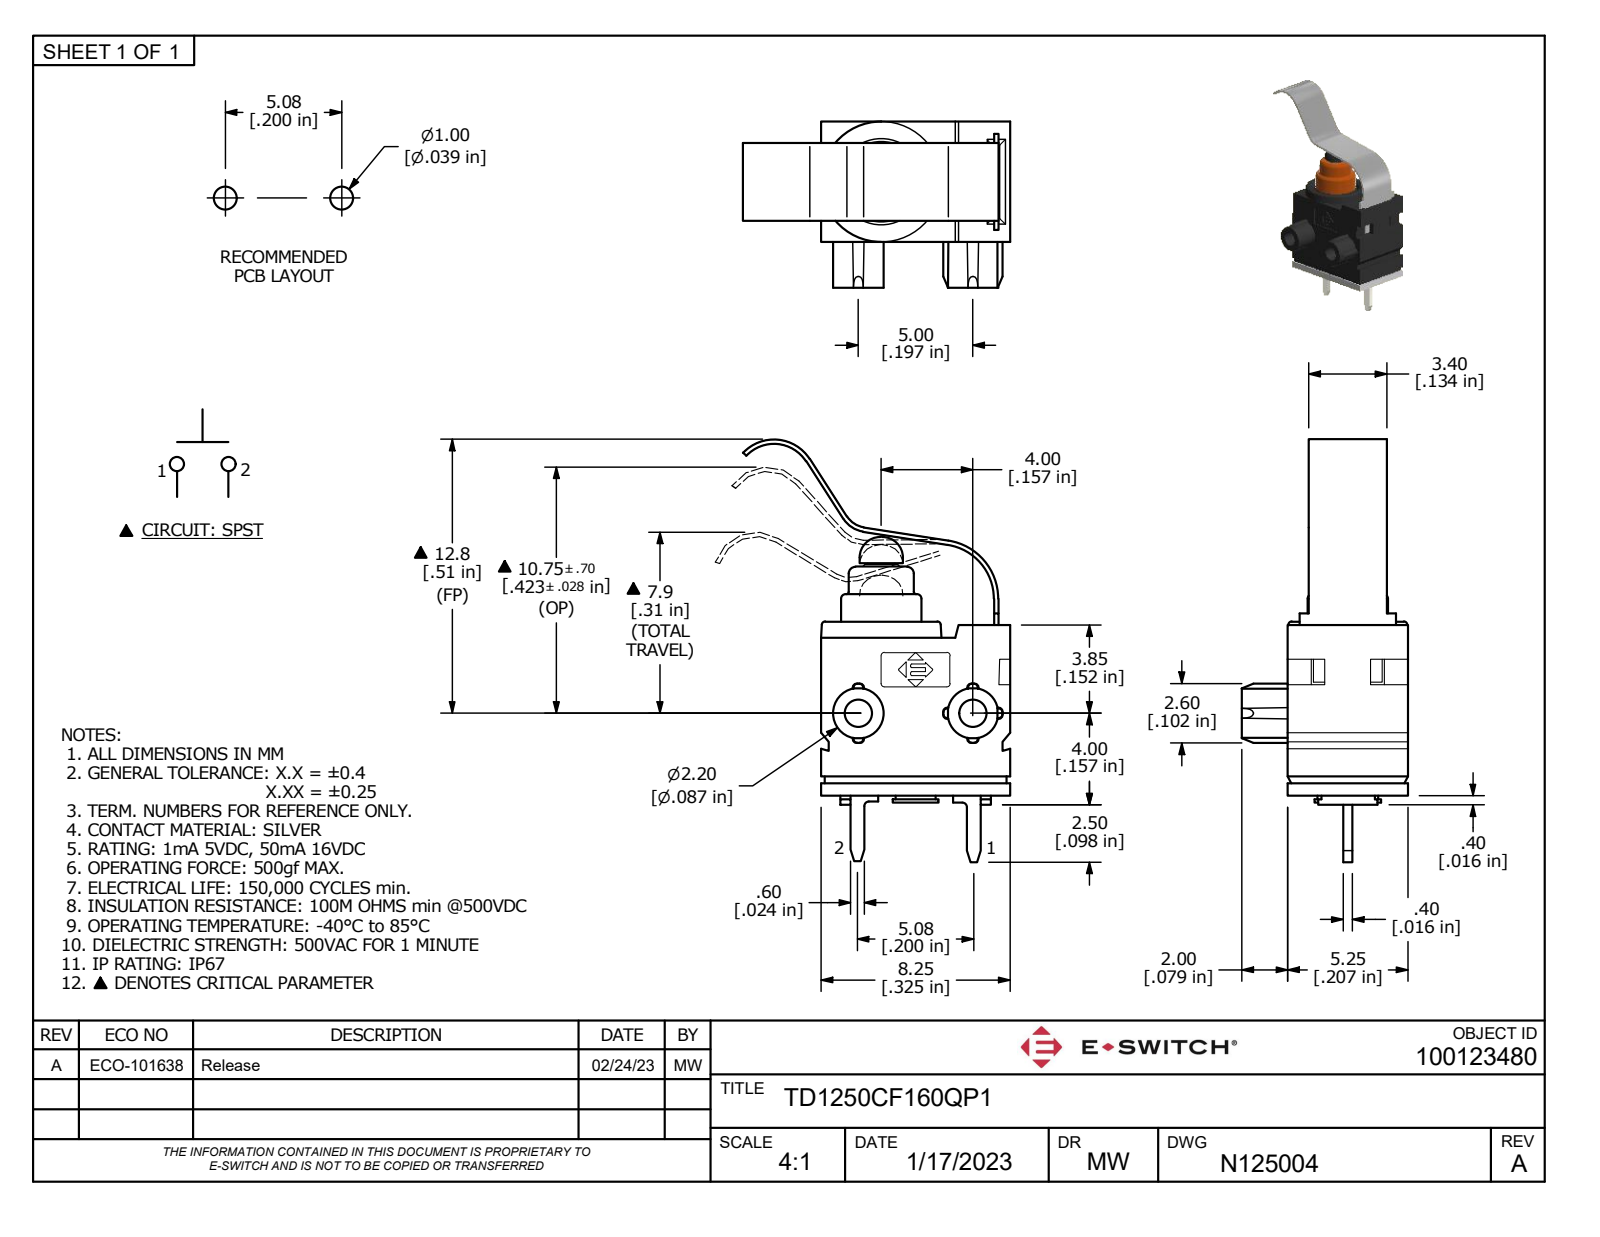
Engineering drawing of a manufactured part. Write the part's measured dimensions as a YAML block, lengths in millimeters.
part_name: "TD1250CF160QP1"
step_written_by: "Autodesk Inventor 2022 (AUTOMOTIVE_DESIGN)"
units: millimeters
bodies: {solids: 1, faces: 249, planar: 191, cylindrical: 46, other: 12}
overall_size: [18.46, 11.66, 7.25]
volume: 359
surface_area: 569
round_holes:
  - {diameter: 1.2, count: 2}
  - {diameter: 4.65, count: 1}
round_bosses_or_shafts:
  - {diameter: 4.5, count: 1}
  - {diameter: 3.5, count: 1}
  - {diameter: 2.85, count: 1}
  - {diameter: 2.2, count: 1}
  - {diameter: 1.9, count: 1}
  - {diameter: 1.2, count: 1}
partial_cylinders:
  - {radius: 0.2, count: 14}
  - {radius: 0.15, count: 4}
  - {radius: 1.06, count: 1}
  - {radius: 1.1, count: 1}
  - {radius: 1.25, count: 1}
  - {radius: 1.67, count: 1}
  - {radius: 1.86, count: 1}
  - {radius: 2.38, count: 1}
face_to_face_distances: [5.24, 8.24, 0.5, 0.55, 6.9, 0.69, 7.55, 7.45, 7.74, 7.24]
hole_center_spacings: [5]
